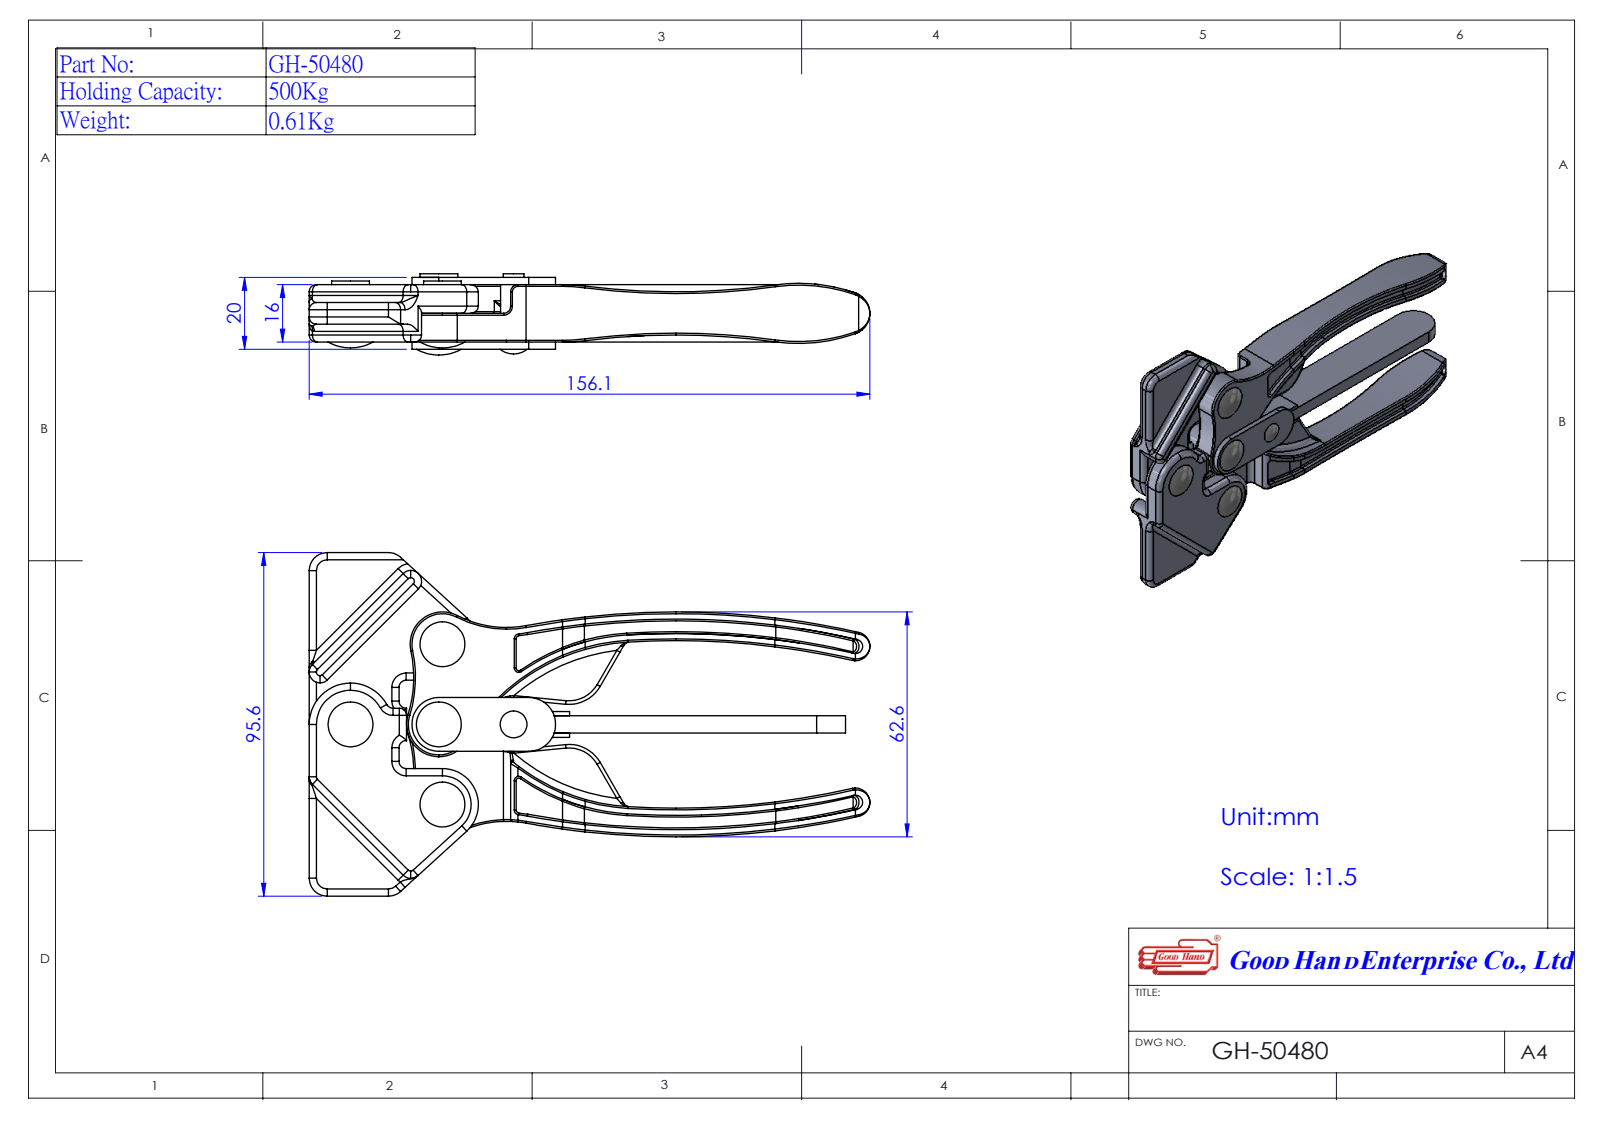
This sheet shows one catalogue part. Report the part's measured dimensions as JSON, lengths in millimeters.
{"part_name": "GH-50480(簡化); 25048002-2^GH-50480(簡化); Group2^GH-50480(簡化); Group1^GH-50480(簡化) (+2 more)", "step_written_by": "SolidWorks 2016 (AUTOMOTIVE_DESIGN)", "units": "millimeters", "bodies": {"solids": 11, "faces": 382, "planar": 99, "cylindrical": 201, "other": 82}, "overall_size": [156.1, 95.6, 22.6], "volume_mm3": 80370, "surface_area_mm2": 40494, "round_holes": [[8, 4], [4.8, 1]], "round_bosses_or_shafts": [[10.5, 4], [23, 1], [18, 1], [5.8, 1]], "partial_cylinders_radius": [[2, 14], [1, 8], [5, 6], [3, 4], [10, 4], [48, 4], [4, 3], [1.25, 2]], "face_to_face_distances": [8, 16, 3, 6, 5, 11, 4.8, 1.5, 2, 4.5], "hole_center_spacings": [22.32, 29.82, 33.95, 20.8, 24.6, 44.6, 45.4]}
